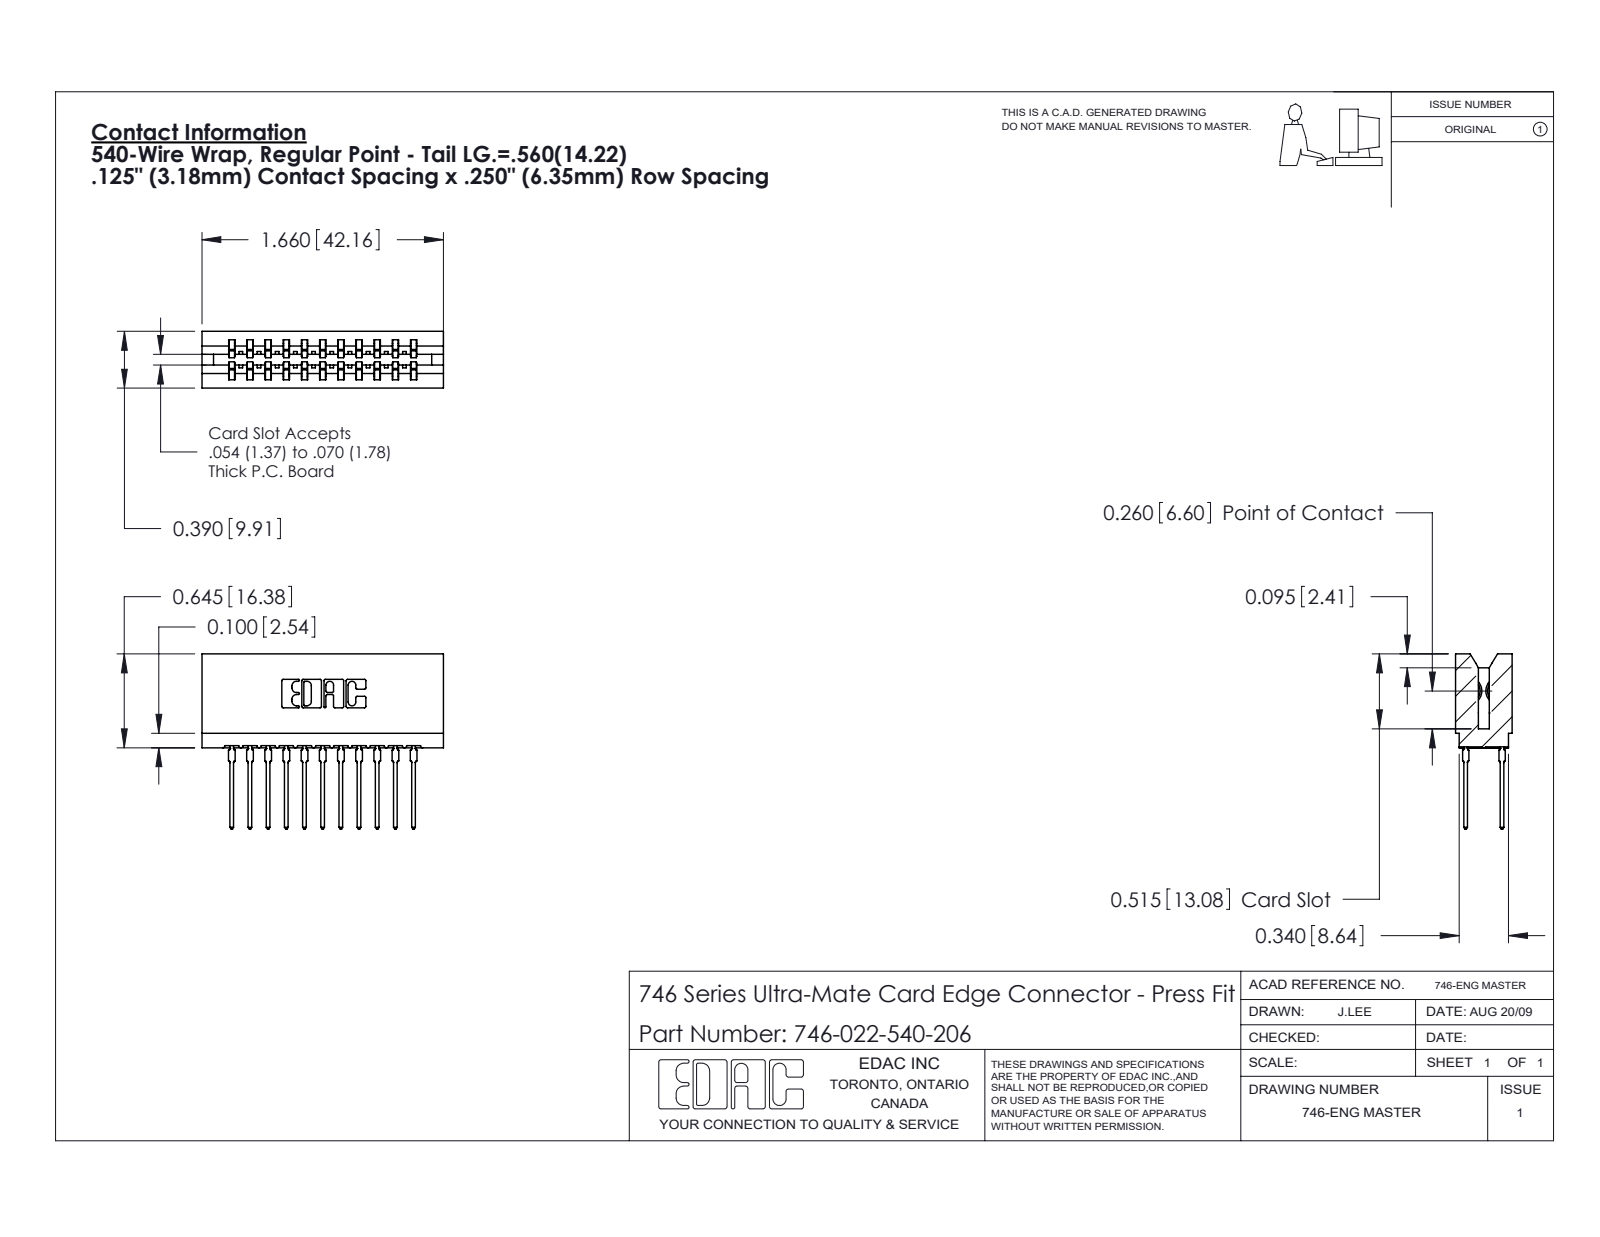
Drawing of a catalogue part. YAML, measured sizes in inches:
part_name: "746 Part_.515 Slot Depth - 06; 746-292-001_540; 746-022-540-206"
step_written_by: "SolidWorks 2020 (CONFIG_CONTROL_DESIGN)"
units: inches
bodies: {solids: 23, faces: 2067, planar: 1068, cylindrical: 427, other: 572}
overall_size: [1.66, 1.204, 0.39]
volume: 0.291
surface_area: 11.4
partial_cylinders:
  - {radius: 0.021, count: 44}
  - {radius: 0.01, count: 22}
  - {radius: 0.015, count: 12}
  - {radius: 0.005, count: 8}
  - {radius: 0.011, count: 8}
  - {radius: 0.007, count: 6}
  - {radius: 0.031, count: 6}
  - {radius: 0.026, count: 3}
face_to_face_distances: [0.25, 0.333, 0.057, 0.5, 0.125, 0.125, 0.083, 0.39, 0.042, 0.208]
